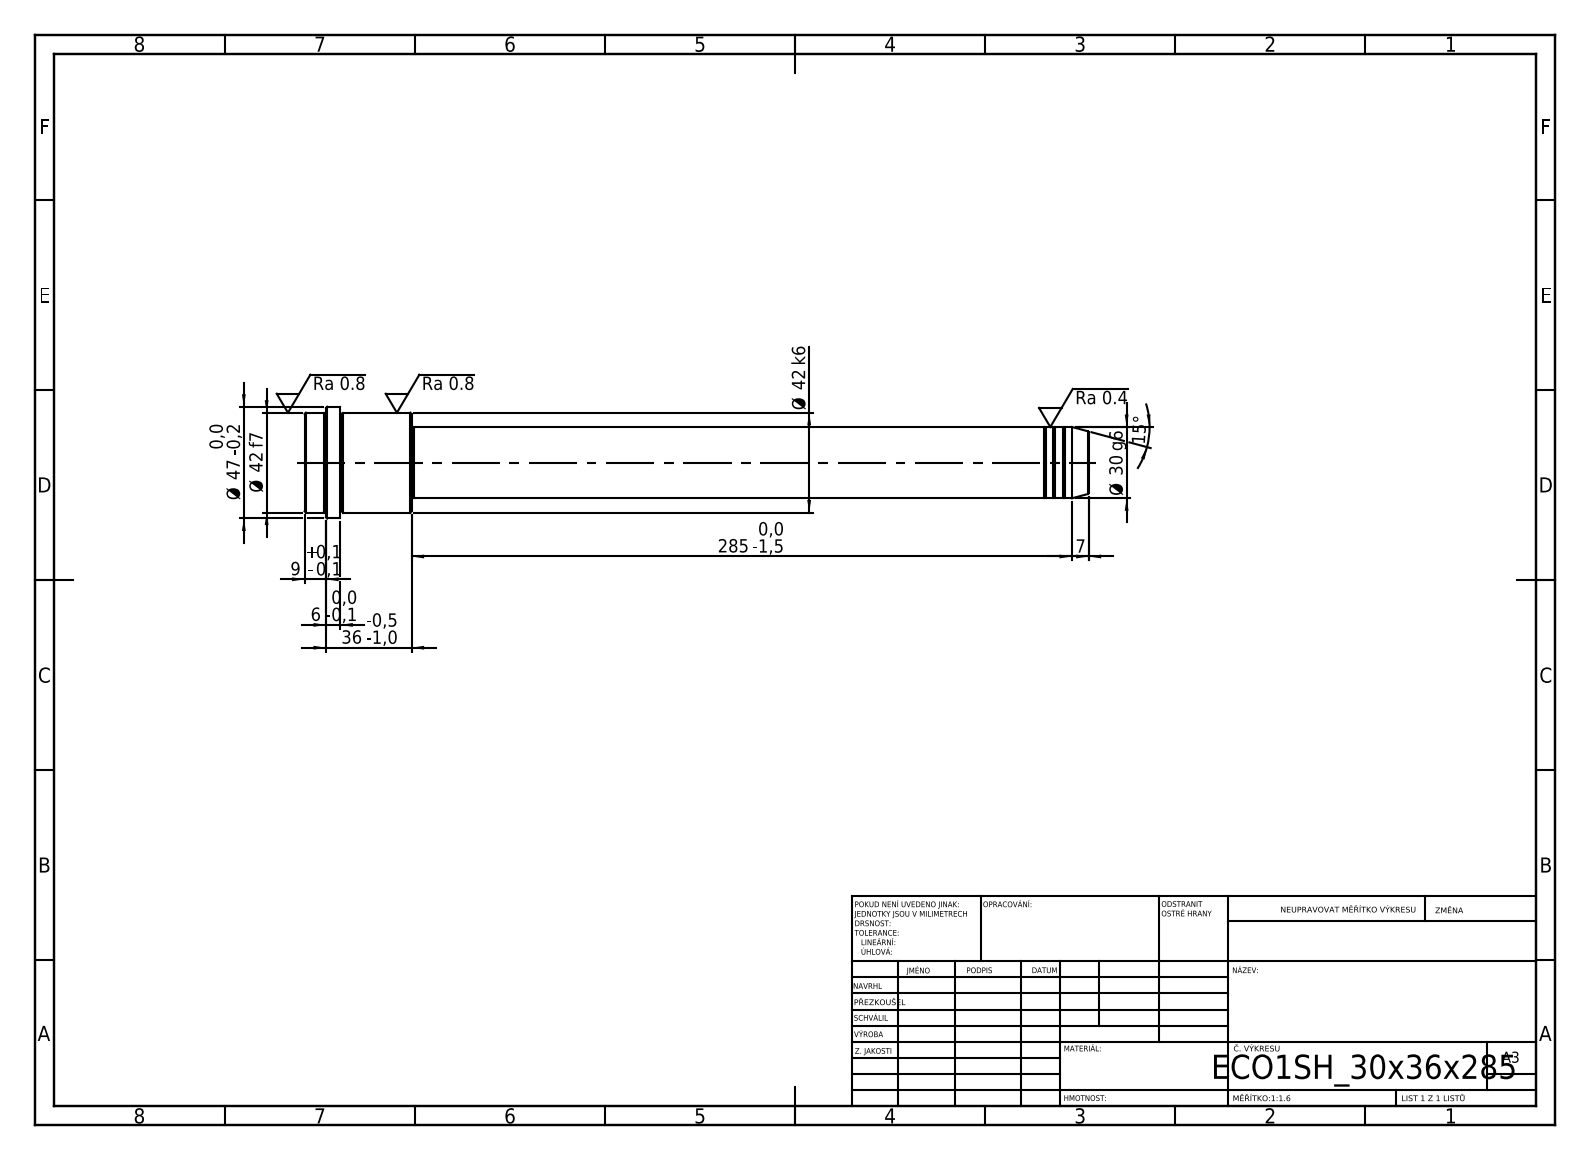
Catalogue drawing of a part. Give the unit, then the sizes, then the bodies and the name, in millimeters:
Units: millimetres
Overall size (bounding box): 330 × 47 × 47
Round bosses / shafts (diameter × count): ⌀47 ×1, ⌀42 ×1, ⌀30 ×1, ⌀29 ×1
Main face-to-face distances: 45, 285, 330, 315, 30, 15, 321, 36, 6, 9
Volume: 264 992 mm³ · Surface area: 36 432 mm²
Bodies: 1 solid, 52 faces (6 planar, 16 cylindrical, 30 other)
STEP written by: SolidWorks 2019 (CONFIG_CONTROL_DESIGN)
